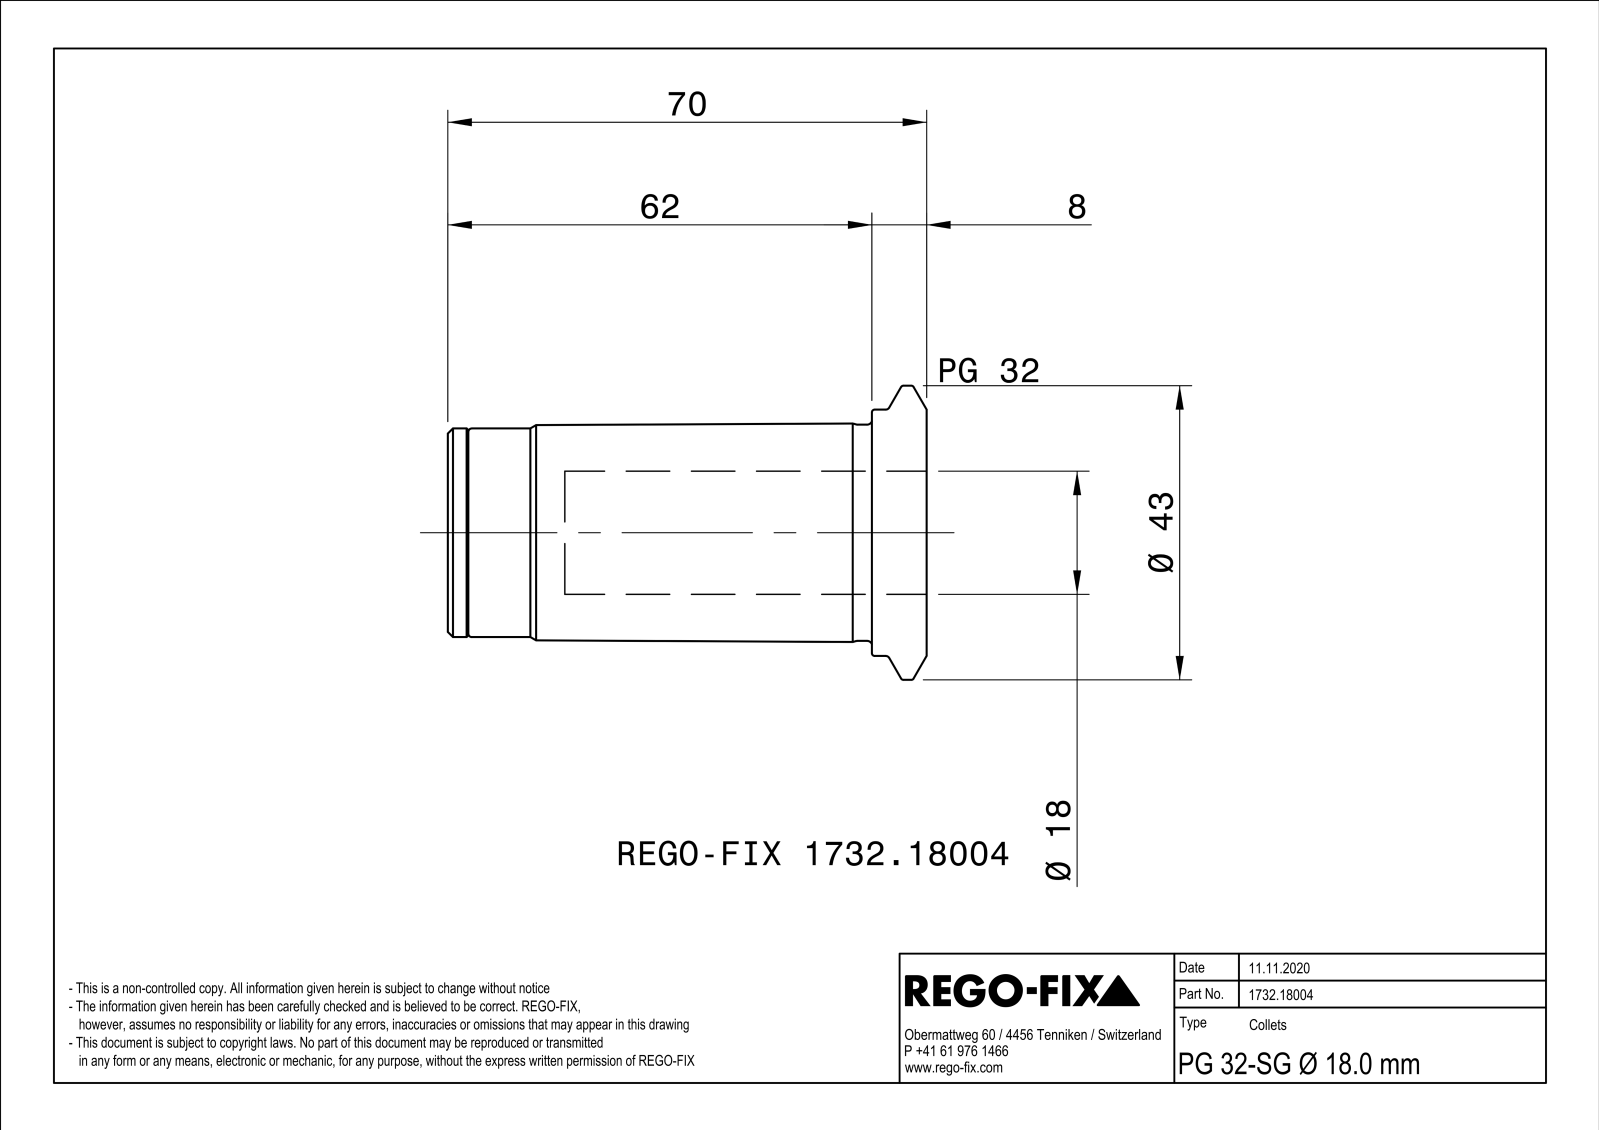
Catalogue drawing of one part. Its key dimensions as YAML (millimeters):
part_name: "NOCUT"
step_written_by: "SIEMENS PLM Software Solid Edge ST10 (AUTOMOTIVE_DESIGN)"
units: millimeters
bodies: {solids: 1, faces: 125, planar: 31, cylindrical: 40, other: 54}
overall_size: [70, 43, 42.99]
volume: 39102
surface_area: 16552
round_holes:
  - {diameter: 4, count: 3}
  - {diameter: 8.92, count: 1}
  - {diameter: 10.5, count: 1}
  - {diameter: 18, count: 1}
  - {diameter: 26.92, count: 1}
  - {diameter: 28.5, count: 1}
round_bosses_or_shafts:
  - {diameter: 43, count: 1}
  - {diameter: 36, count: 1}
  - {diameter: 31.6, count: 1}
  - {diameter: 30.5, count: 1}
  - {diameter: 26.5, count: 1}
  - {diameter: 21, count: 1}
partial_cylinders:
  - {radius: 2, count: 6}
  - {radius: 3.5, count: 3}
  - {radius: 3.98, count: 1}
  - {radius: 4.75, count: 1}
  - {radius: 8.75, count: 1}
face_to_face_distances: [1, 70, 58, 12, 59, 11, 8, 60, 2, 10]
hole_center_spacings: [7.75, 13.42, 13.43]
